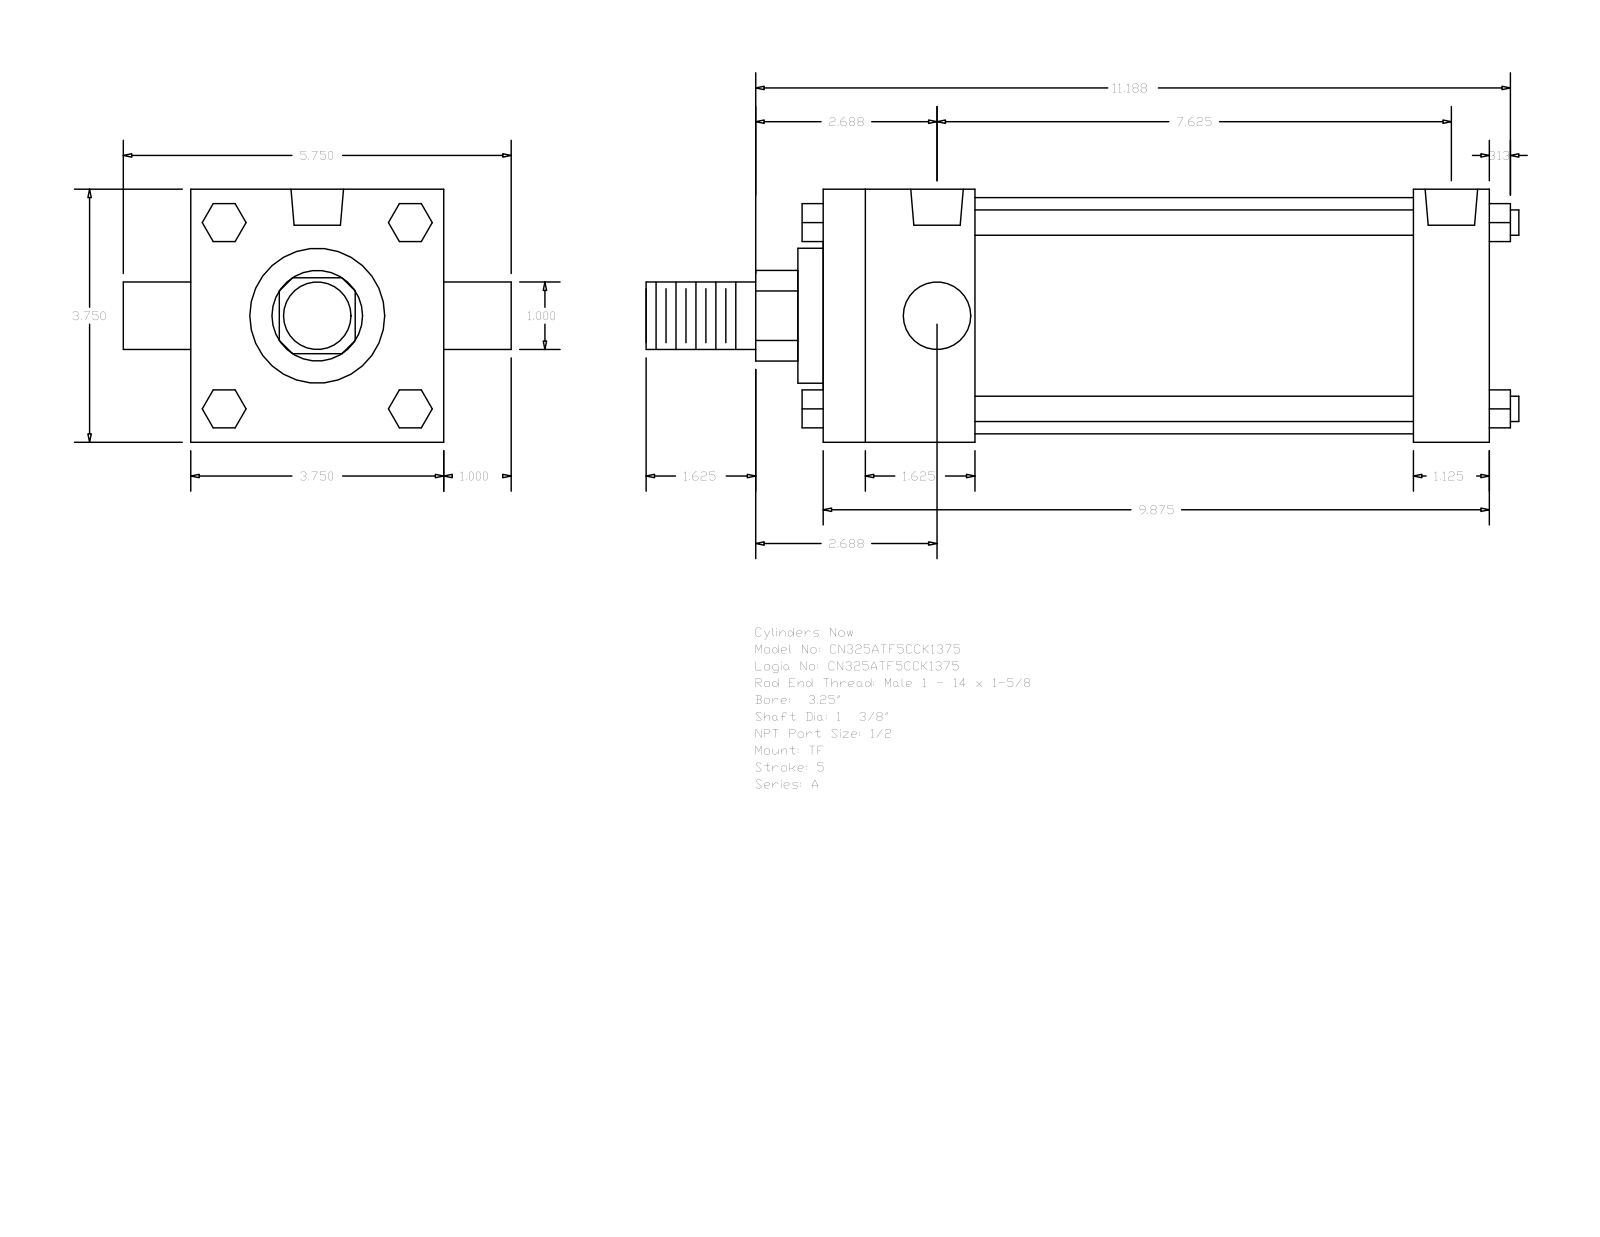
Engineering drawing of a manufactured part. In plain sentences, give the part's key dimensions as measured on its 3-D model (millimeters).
The part is named "A_TF__0325_1.375". Its 3-D file was written by "GSSL Pune (CONFIG_CONTROL_DESIGN)". It is 0 solids with 120 faces: 92 planar, 28 cylindrical and 0 other. Overall it measures 328.61 by 146.05 by 95.25 millimeters. Round holes: 3 of diameter 8.73, 2 of diameter 19.77. Round bosses or shafts: 4 of diameter 9.53, 2 of diameter 25.4, 1 of diameter 88.9, 1 of diameter 50.8, 1 of diameter 34.92. Partial cylindrical surfaces (rounded edges, fillets, slot ends): 1 of radius 17.06. The main face-to-face distances are 95.24, 250.83, 57.15, 28.58, 222.25, 165.1, 193.68, 66.67, 9.52, 231.77. The hole center spacings are 3.18, 190.5, 187.32, 193.68.
